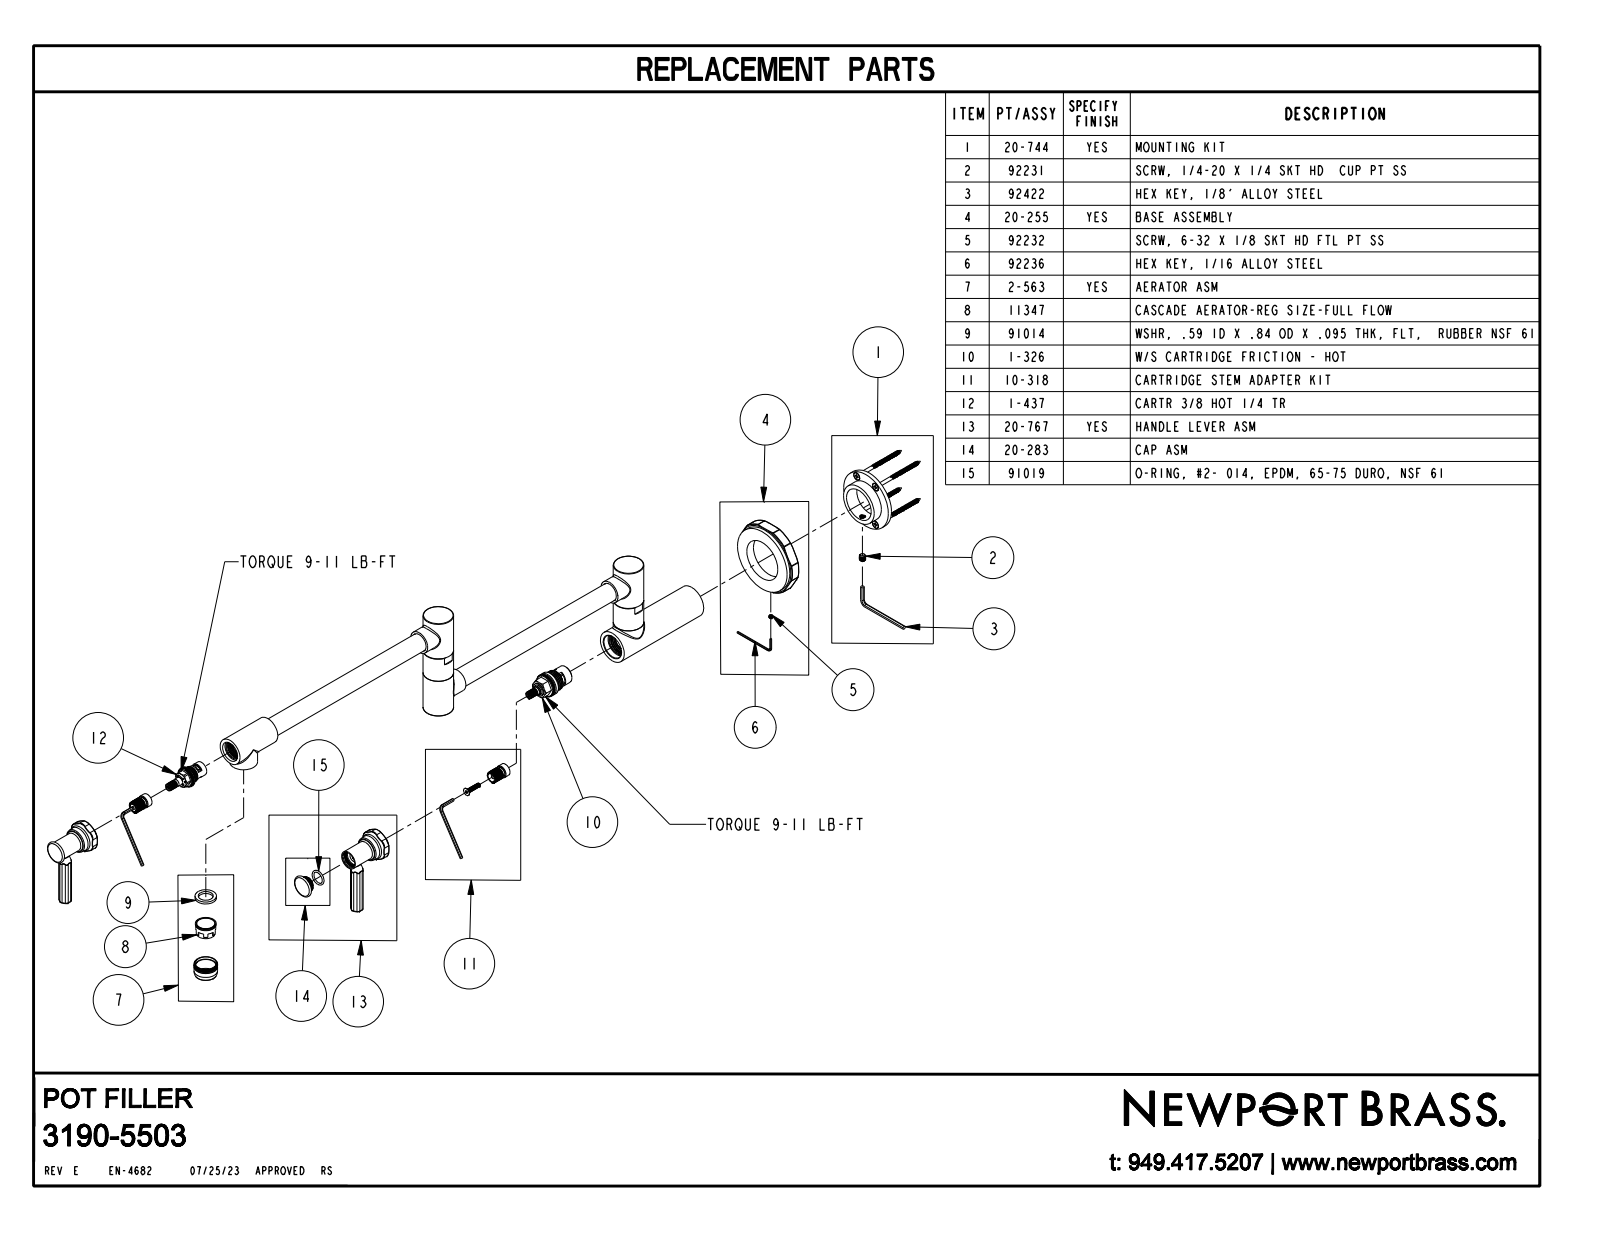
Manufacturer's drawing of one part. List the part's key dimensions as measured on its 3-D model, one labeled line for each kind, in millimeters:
Part name (STEP PRODUCT): 3190-5503
STEP written by: CREO PARAMETRIC BY PTC INC, 2018400 (CONFIG_CONTROL_DESIGN)
Units: millimetres
Bodies: 1 solid, 470 faces (80 planar, 93 cylindrical, 297 other)
Overall size (bounding box): 697.1 × 227.6 × 75.7
Volume: 516 000 mm³ · Surface area: 89 740 mm²
Round bosses / shafts (diameter × count): ⌀23.9 ×4, ⌀30.5 ×2, ⌀27.9 ×2, ⌀19.3 ×2, ⌀19.1 ×2, ⌀69.9 ×1, ⌀33.7 ×1, ⌀20 ×1
Partial cylindrical surfaces — rounded edges, fillets, slot ends (radius × count): R2 ×12, R3 ×12, R7.9 ×12, R0.5 ×11, R12 ×1, R37.8 ×1
Main face-to-face distances: 14.5, 72.6, 40, 112.7, 11.9, 72.6, 539.7, 42.6, 45.1, 0.5
